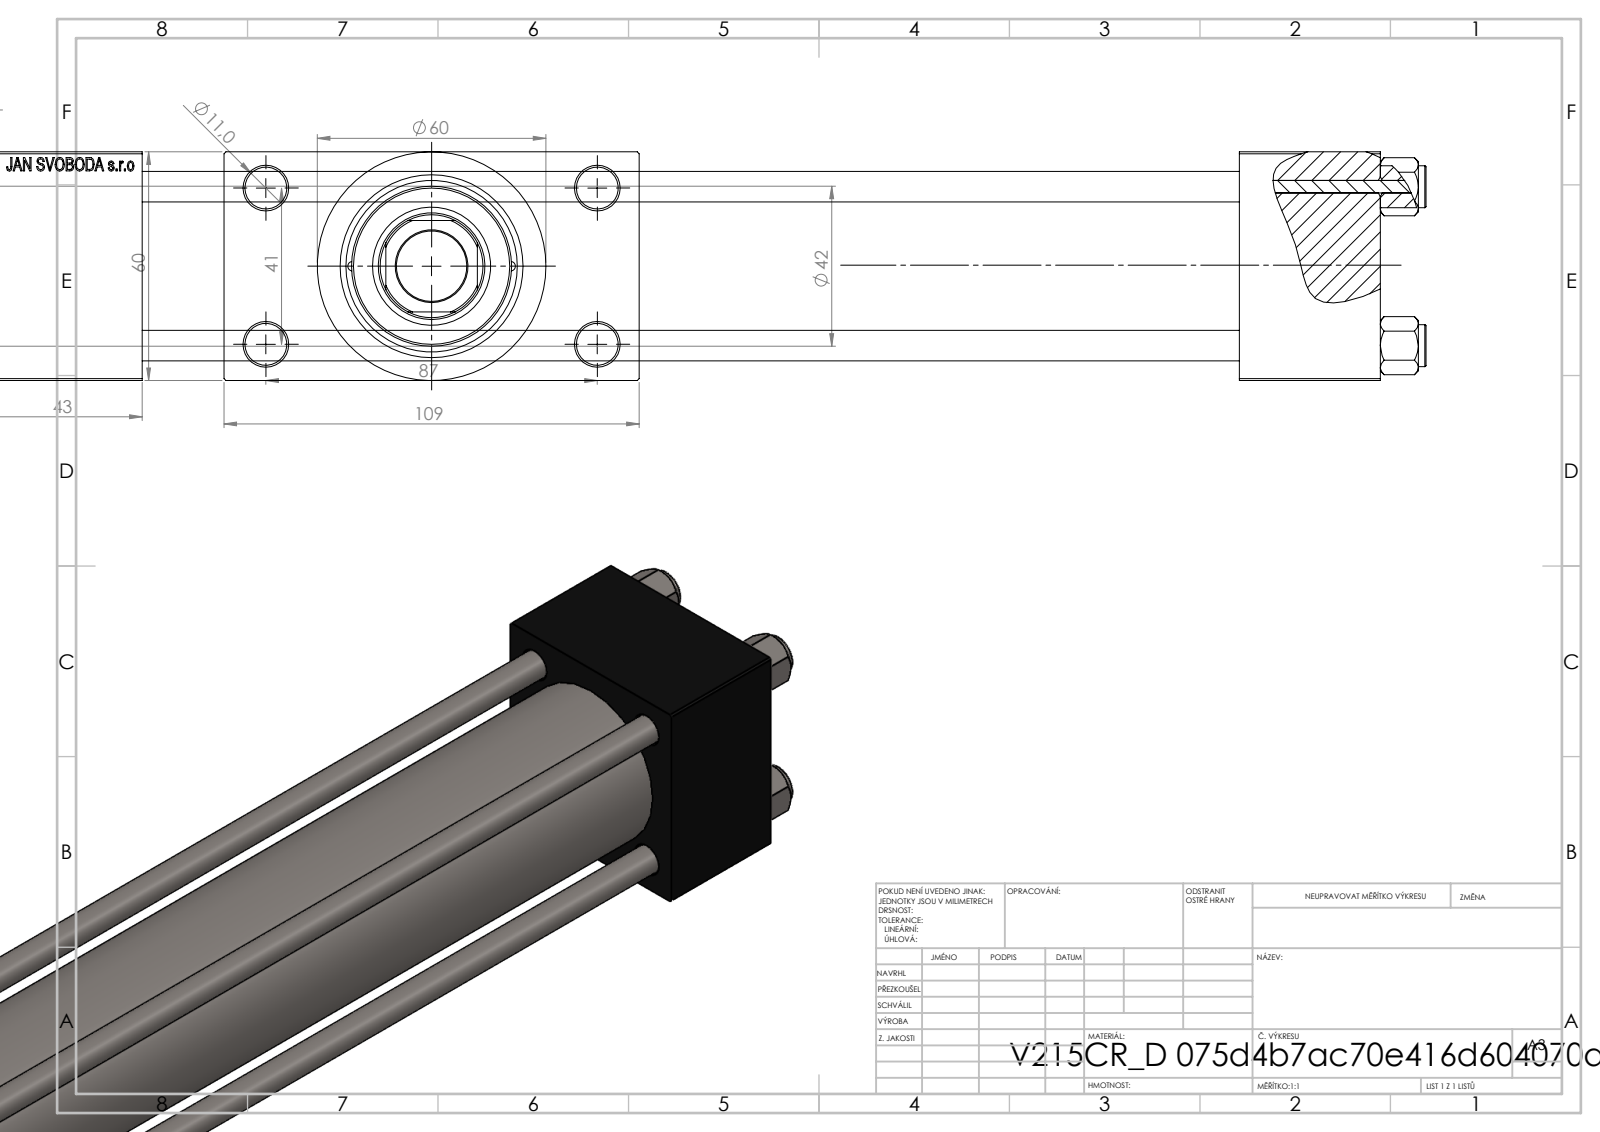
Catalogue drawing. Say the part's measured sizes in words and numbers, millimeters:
The part is named "V215CR_D_Body; V215CR_D_TYCINKA; NUT_M5_D; V215_VC_A (+1 more)". Its 3-D file was written by "SolidWorks 2019 (CONFIG_CONTROL_DESIGN)". It is 11 solids with 1114 faces: 502 planar, 92 cylindrical and 520 other. Overall it measures 415 by 109 by 60 millimeters. Its volume is 809 743 cubic millimeters and its surface area 234 570 square millimeters. Round holes: 4 of diameter 8, 4 of diameter 11, 2 of diameter 2.5, 2 of diameter 7, 2 of diameter 16.66, 2 of diameter 24, 1 of diameter 18.5, 1 of diameter 28, 1 of diameter 31, 1 of diameter 40, 1 of diameter 45. Round bosses or shafts: 4 of diameter 11, 1 of diameter 60, 1 of diameter 46, 1 of diameter 42. Partial cylindrical surfaces (rounded edges, fillets, slot ends): 1 of radius 13.5. The main face-to-face distances are 60, 288, 24.5, 84.5, 37, 325, 368, 331, 43, 109. The hole center spacings are 20.85, 22.65, 29.49, 30.62, 41.7, 46.53, 47.15, 48.09.
